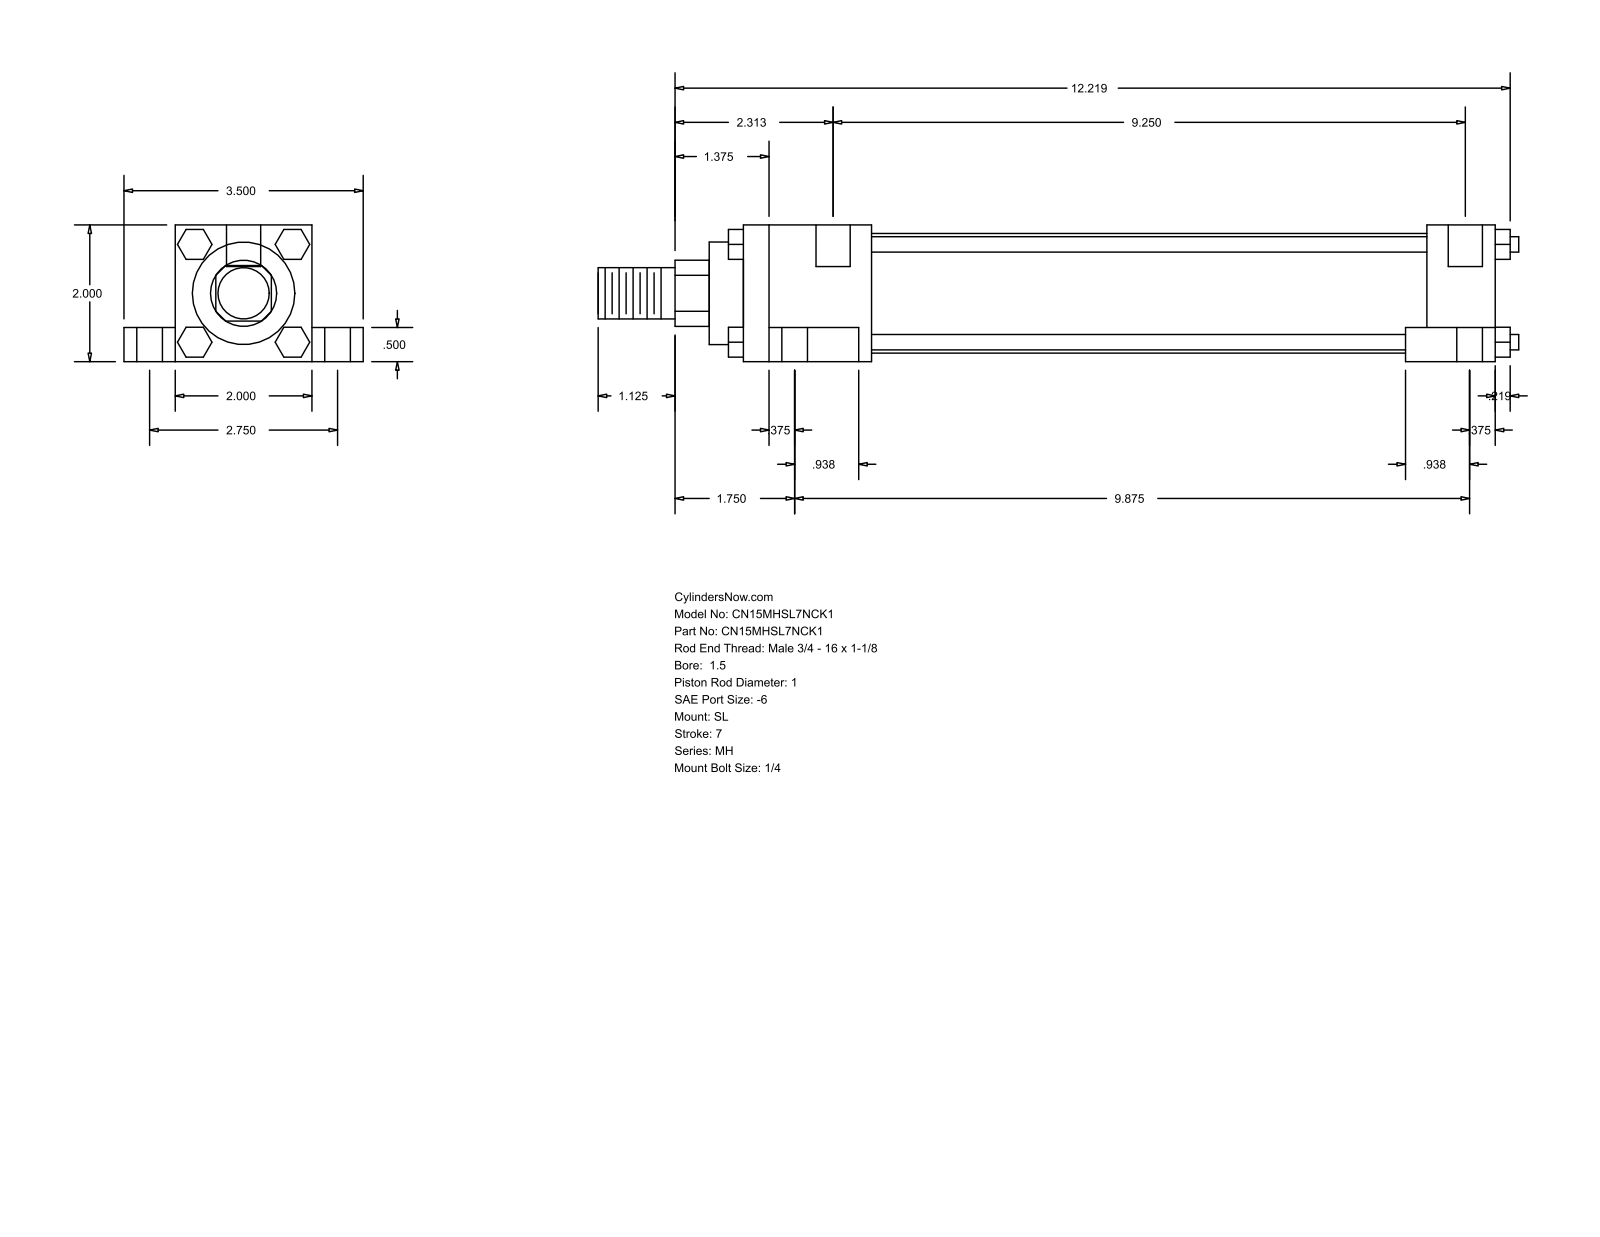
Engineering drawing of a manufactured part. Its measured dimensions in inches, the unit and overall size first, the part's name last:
Units: inches
Overall size (bounding box): 13.469 × 3.5 × 2
Round holes (diameter × count): ⌀0.219 ×4, ⌀0.375 ×4, ⌀0.625 ×4, ⌀0.5 ×2
Round bosses / shafts (diameter × count): ⌀0.225 ×4, ⌀1.75 ×1, ⌀1.5 ×1, ⌀1 ×1, ⌀0.75 ×1
Partial cylindrical surfaces — rounded edges, fillets, slot ends (radius × count): R0.484 ×1
Main face-to-face distances: 2, 0.5, 1.5, 0.75, 2.75, 11, 1, 0.375, 1.313, 9.313
Hole centre spacings: 1.376, 1.443, 1.485, 2.75, 9.375, 9.413, 9.537, 9.875
Bodies: 0 solids, 148 faces (112 planar, 36 cylindrical, 0 other)
Part name (STEP PRODUCT): MH_SL__0150_1
STEP written by: GSSL Pune (CONFIG_CONTROL_DESIGN)
